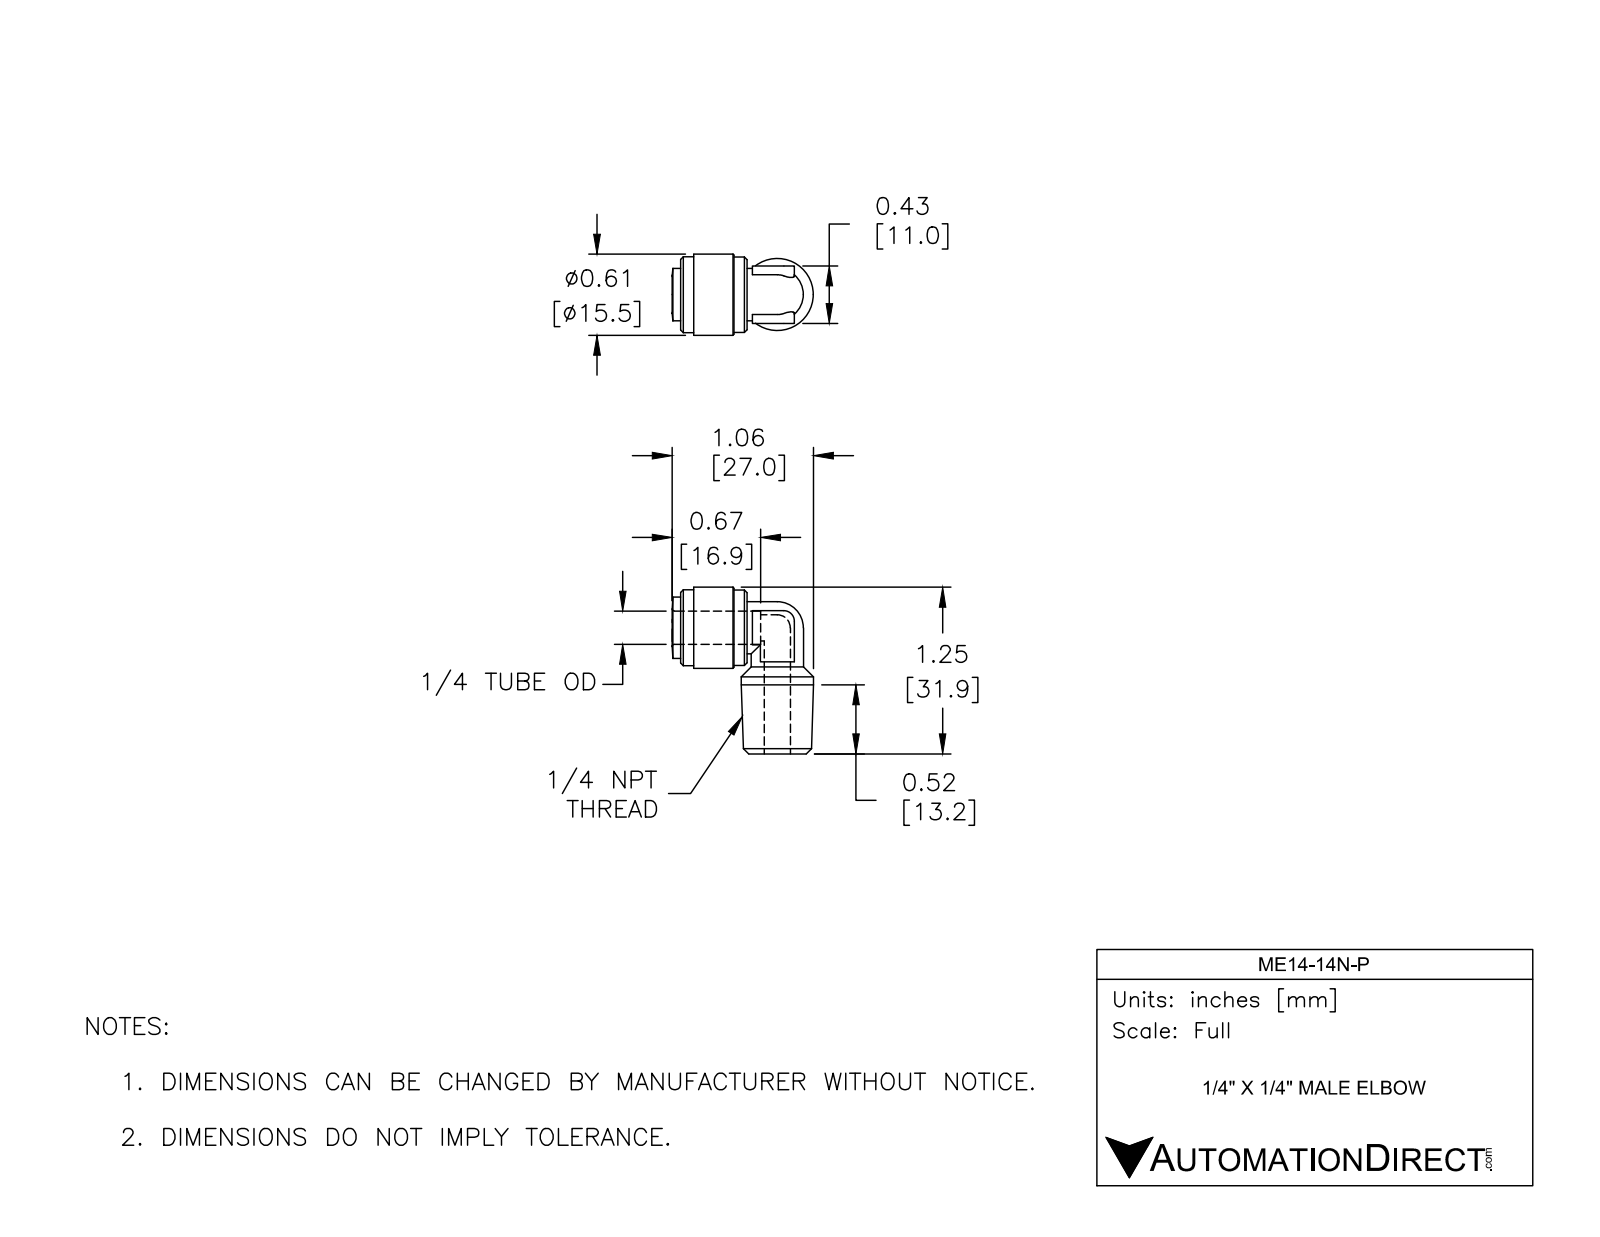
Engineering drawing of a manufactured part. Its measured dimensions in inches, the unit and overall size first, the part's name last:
Units: inches
Overall size (bounding box): 1.254 × 1.063 × 0.61
Round holes (diameter × count): ⌀0.197 ×2, ⌀0.25 ×1
Round bosses / shafts (diameter × count): ⌀0.394 ×2, ⌀0.61 ×1, ⌀0.571 ×1, ⌀0.567 ×1, ⌀0.543 ×1
Partial cylindrical surfaces — rounded edges, fillets, slot ends (radius × count): R0.079 ×1
Main face-to-face distances: 0.433, 0.5, 0.098, 0.402, 0.856, 0.356, 0.758, 1.077, 0.256, 0.303
Volume: 0.29 in³ · Surface area: 4.569 in²
Bodies: 1 solid, 62 faces (20 planar, 20 cylindrical, 22 other)
Part name (STEP PRODUCT): ME14-14N-P
STEP written by: SolidWorks 2017 (AUTOMOTIVE_DESIGN)
